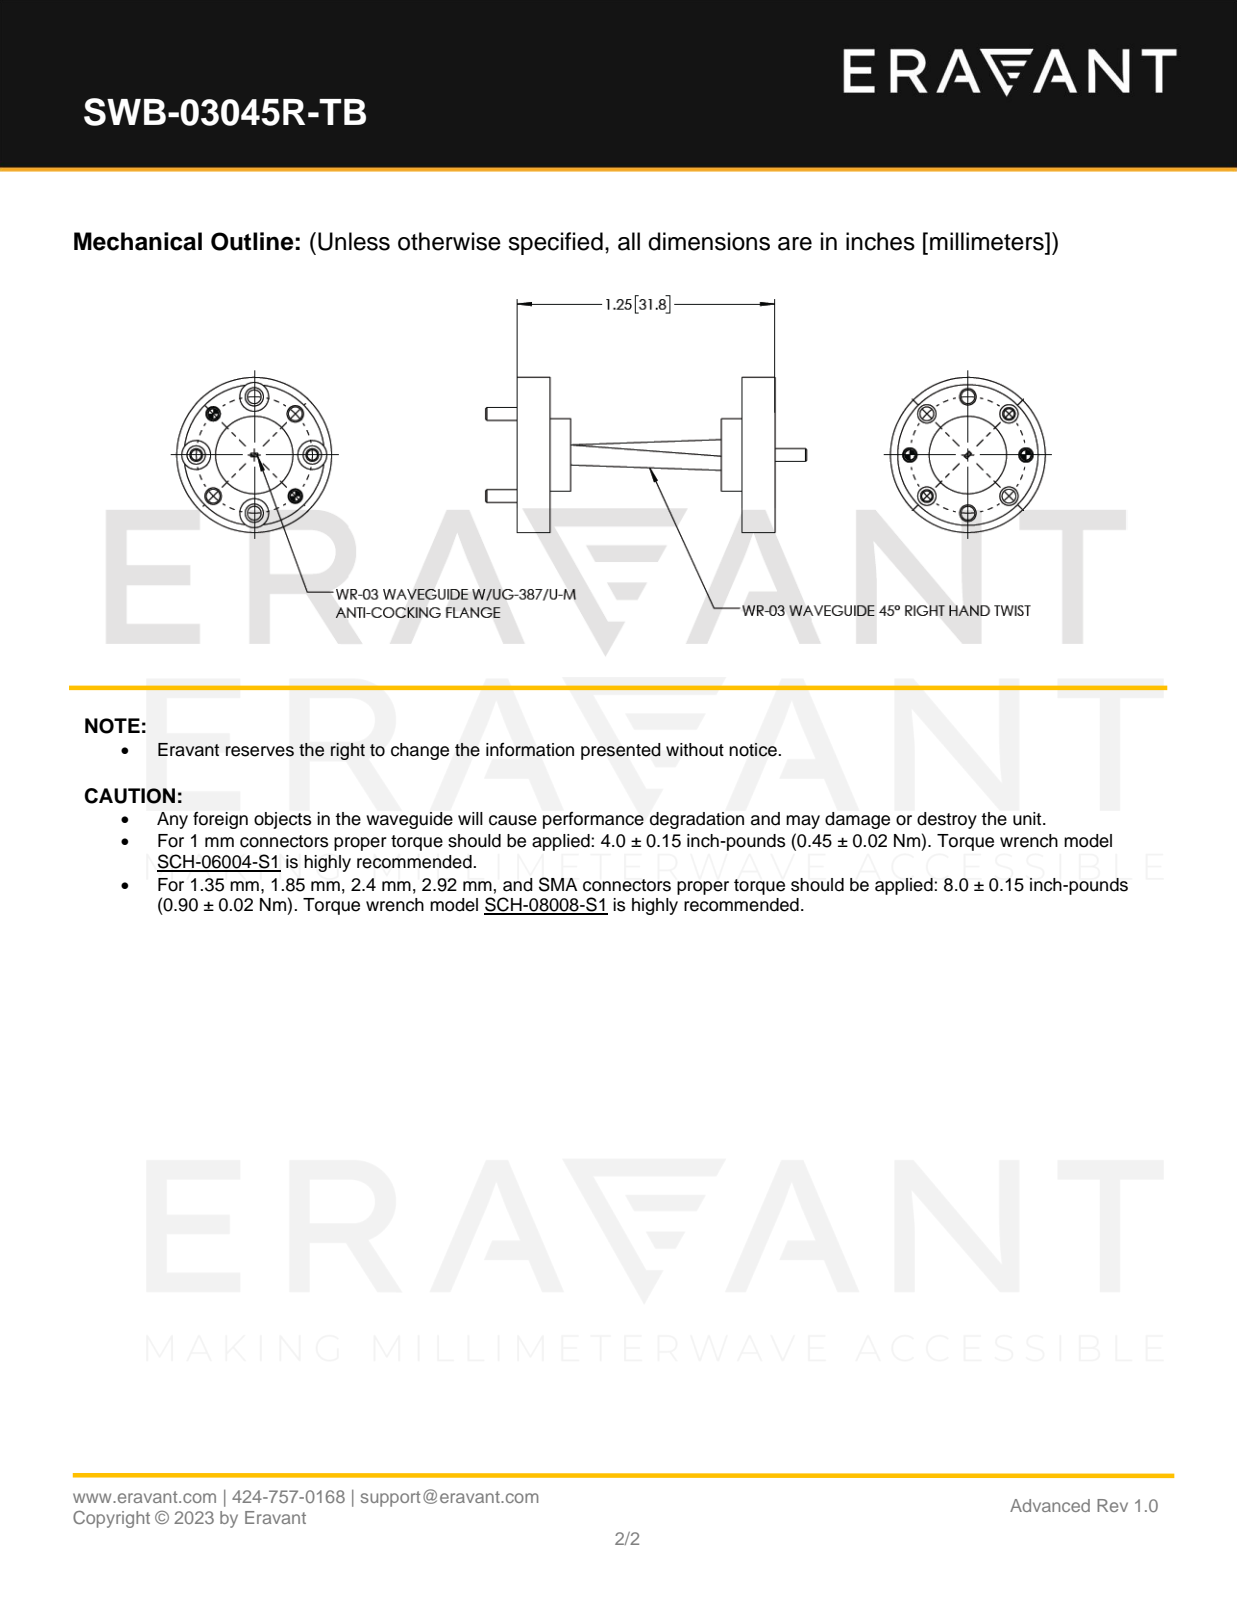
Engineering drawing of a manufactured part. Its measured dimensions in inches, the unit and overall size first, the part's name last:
Units: inches
Overall size (bounding box): 1.555 × 0.75 × 0.75
Round holes (diameter × count): ⌀0.089 ×8, ⌀0.061 ×4, ⌀0.067 ×4, ⌀0.14 ×4, ⌀0.68 ×1
Round bosses / shafts (diameter × count): ⌀0.063 ×4, ⌀0.75 ×1, ⌀0.375 ×1, ⌀0.35 ×1
Main face-to-face distances: 0.14, 1.07, 0.16, 1.09, 0.02, 1.23, 0.93, 0.1, 1.25, 1.21
Hole centre spacings: 0.215, 0.398, 0.281, 0.519, 0.52, 0.281, 0.562, 0.563
Volume: 0.149 in³ · Surface area: 3.94 in²
Bodies: 5 solids, 136 faces (30 planar, 66 cylindrical, 40 other)
Part name (STEP PRODUCT): WB-T03-5R-A, Defeatured
STEP written by: SolidWorks 2021 (AUTOMOTIVE_DESIGN)
